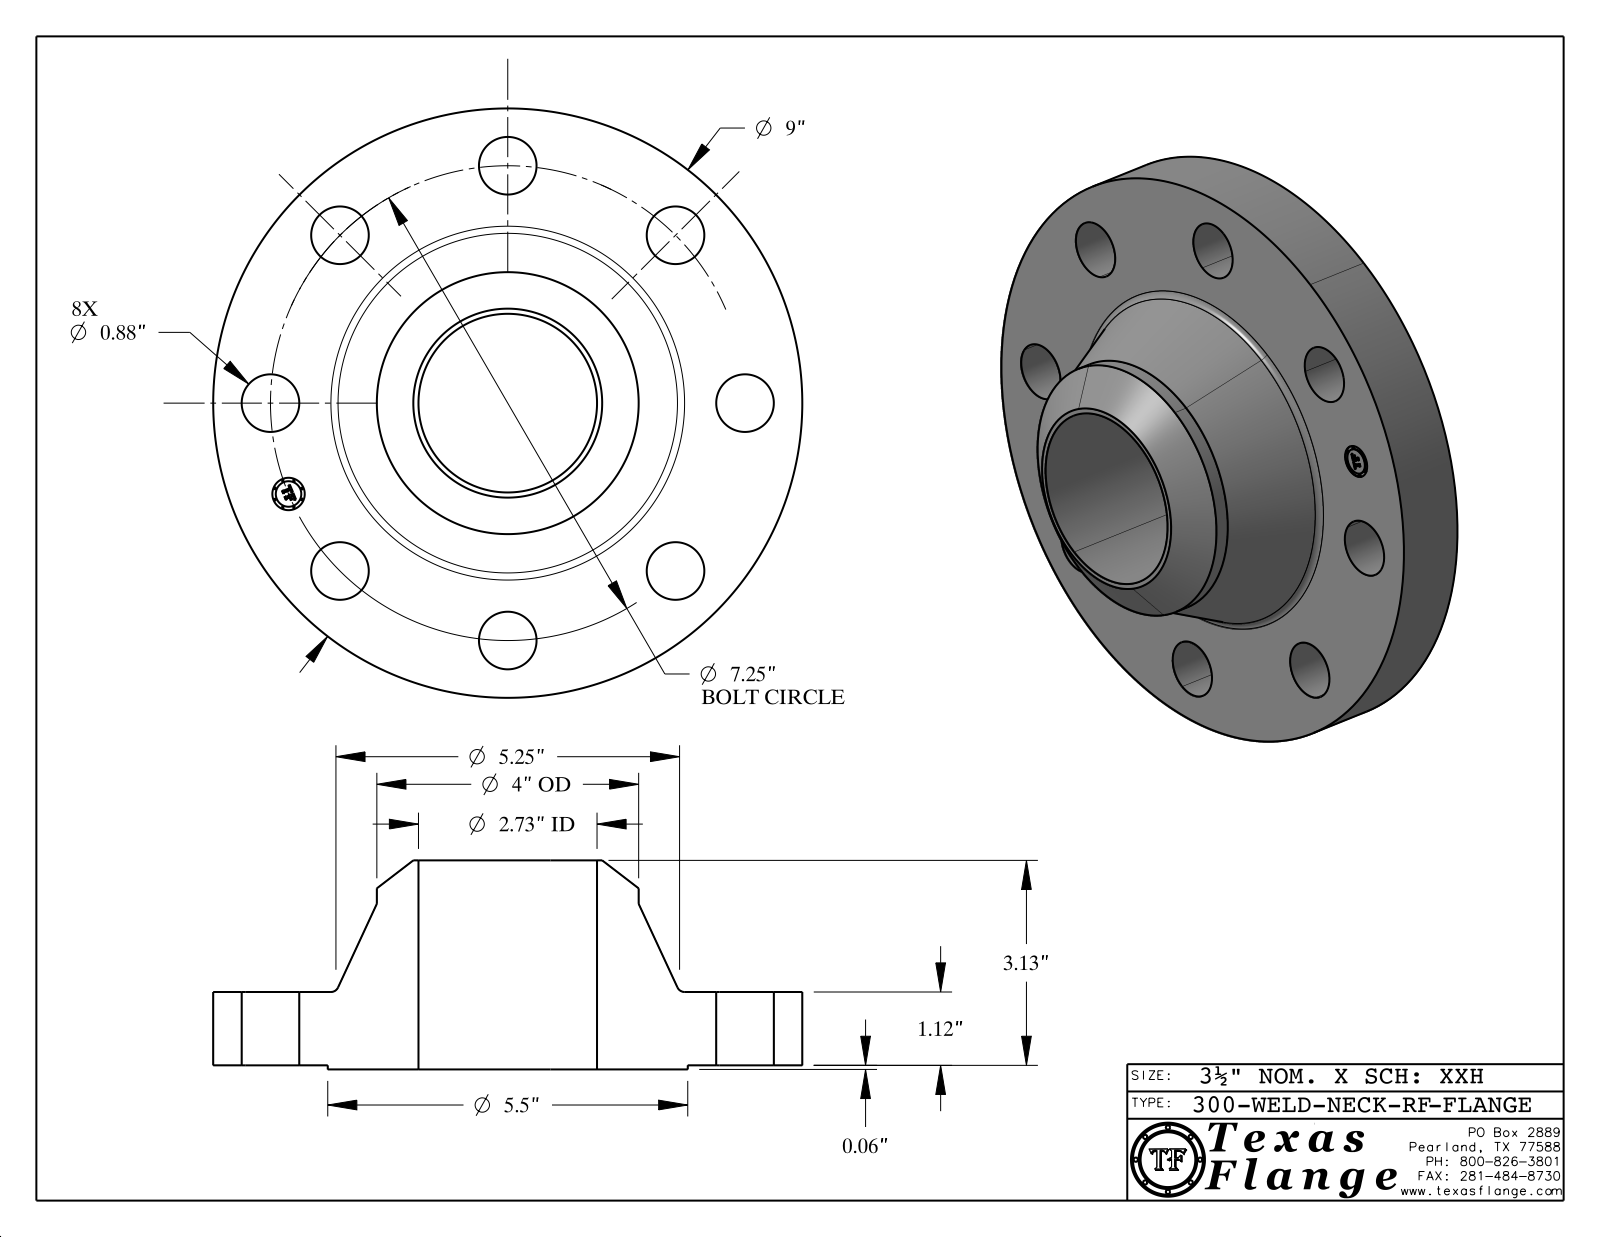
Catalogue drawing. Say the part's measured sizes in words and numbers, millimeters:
The part is named "300-WELD-NECK-RF". Its 3-D file was written by "CATIA V5 STEP AP214 (AUTOMOTIVE_DESIGN)". It is 1 solid with 419 faces: 369 planar, 44 cylindrical and 6 other. Overall it measures 228.6 by 228.6 by 81.1 millimeters. Its volume is 1 284 000 cubic millimeters and its surface area 133 900 square millimeters. Round holes: 8 of diameter 22.4, 1 of diameter 12.6, 1 of diameter 69.3. Round bosses or shafts: 8 of diameter 0.8, 1 of diameter 228.6, 1 of diameter 139.7, 1 of diameter 101.6, 1 of diameter 9.9. The main face-to-face distances are 28.4, 1.6, 30, 81.1, 79.5, 51.1, 29.7, 28.1, 0.4, 51.4. The hole center spacings are 92.1, 70.5, 130.2, 170.1, 184.2, 35.9, 180.6, 102.3.
